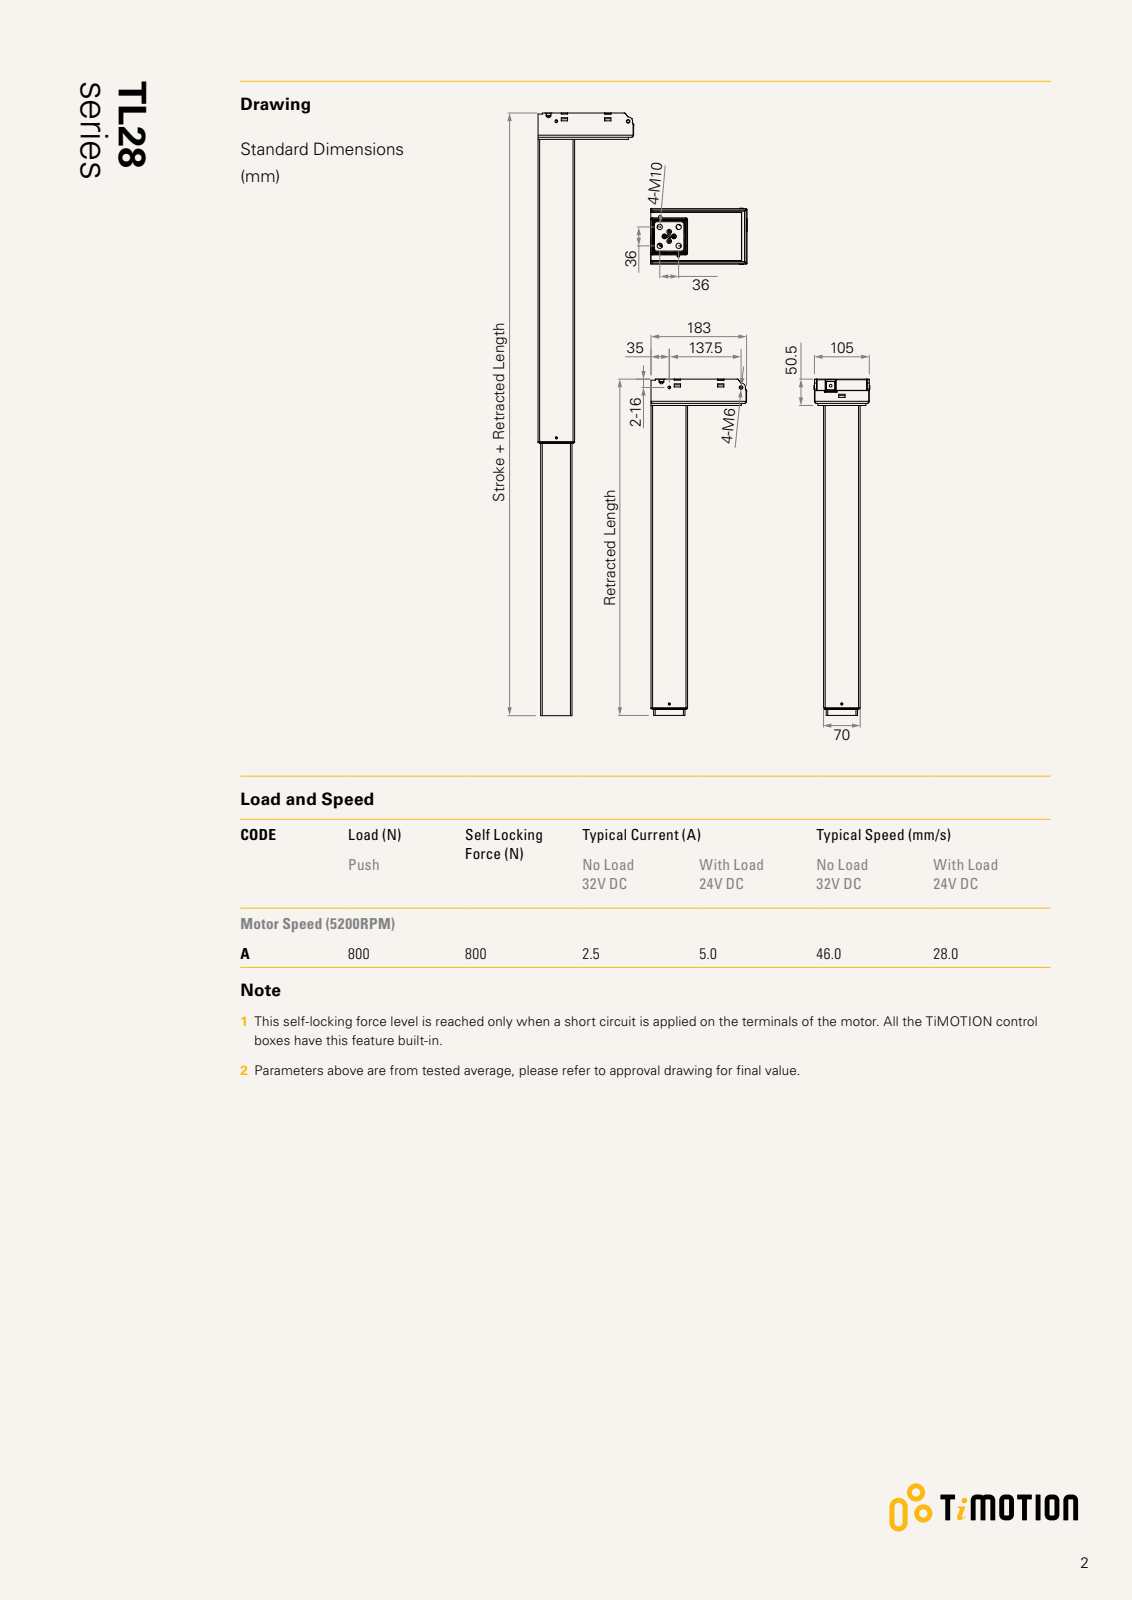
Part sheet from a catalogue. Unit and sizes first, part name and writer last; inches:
Units: inches
Overall size (bounding box): 25.394 × 7.205 × 4.213
Round holes (diameter × count): ⌀0.197 ×4, ⌀0.354 ×4, ⌀0.205 ×2, ⌀0.315 ×1, ⌀0.472 ×1
Round bosses / shafts (diameter × count): ⌀0.346 ×2, ⌀0.197 ×2, ⌀0.276 ×1
Partial cylindrical surfaces — rounded edges, fillets, slot ends (radius × count): R0.012 ×22, R0.118 ×12, R0.039 ×9, R0.157 ×4, R0.098 ×3, R0.059 ×2, R0.079 ×2, R0.177 ×1
Main face-to-face distances: 2.756, 0.157, 1.673, 0.315, 0.689, 1.516, 0.161, 3.445, 1.831, 22.972
Hole centre spacings: 0.792, 1.002, 1.278, 1.417, 0.354, 0.748, 1.497, 1.594
Volume: 195.9 in³ · Surface area: 471.2 in²
Bodies: 2 solids, 448 faces (306 planar, 109 cylindrical, 33 other)
Part name (STEP PRODUCT): 產品三維模型圖-TL28（標準）-A
STEP written by: SolidWorks 2015 (AUTOMOTIVE_DESIGN)
